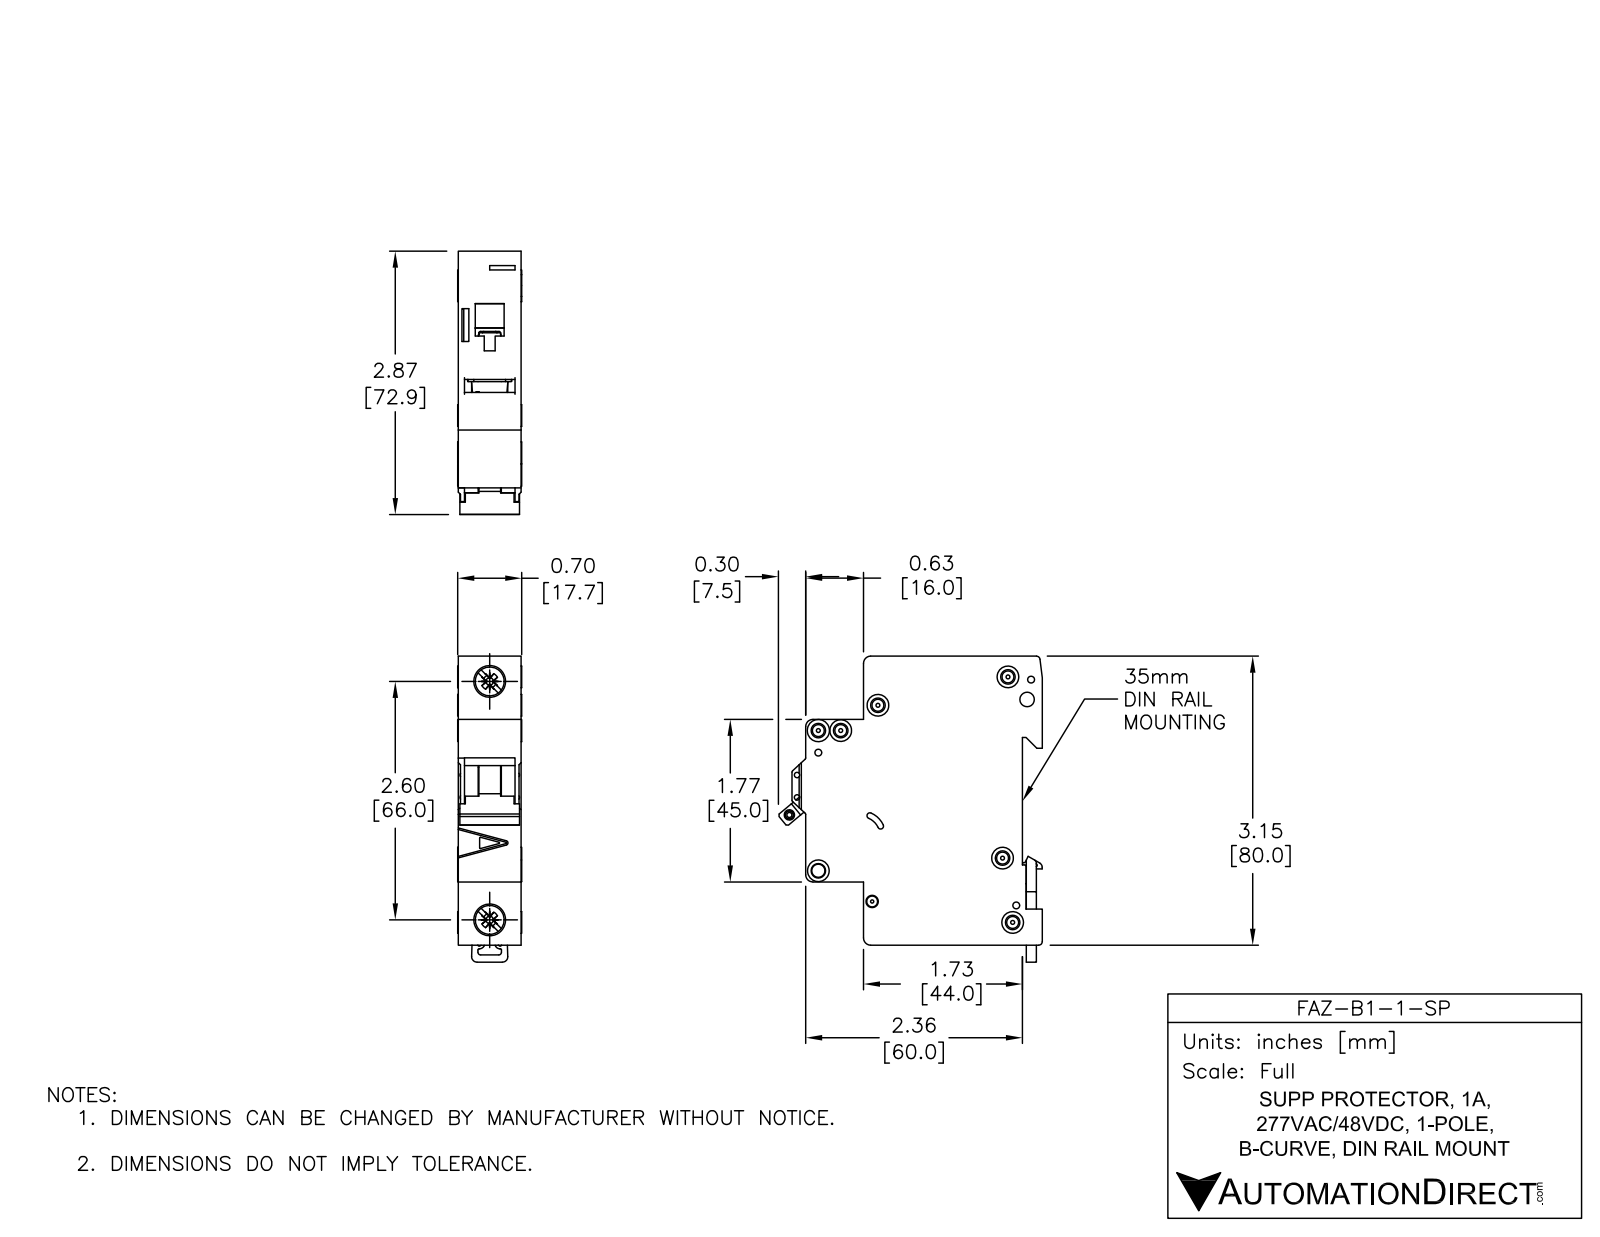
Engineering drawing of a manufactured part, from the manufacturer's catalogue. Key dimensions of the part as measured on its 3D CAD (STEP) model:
Part name (STEP PRODUCT): FAZ-B1-1-SP
STEP written by: SolidWorks 2014 (AUTOMOTIVE_DESIGN)
Units: millimetres
Bodies: 5 solids, 558 faces (235 planar, 202 cylindrical, 121 other)
Overall size (bounding box): 84.78 × 73.04 × 17.7
Volume: 74 935 mm³ · Surface area: 19 545 mm²
Round holes (diameter × count): ⌀3.6 ×6, ⌀1.9 ×3, ⌀1.09 ×2, ⌀1.5 ×2, ⌀4 ×2, ⌀7.15 ×2, ⌀2.15 ×1, ⌀2.2 ×1, ⌀2.55 ×1, ⌀3.3 ×1, ⌀3.4 ×1
Round bosses / shafts (diameter × count): ⌀6 ×4, ⌀8.2 ×2, ⌀2.5 ×1
Partial cylindrical surfaces — rounded edges, fillets, slot ends (radius × count): R0.25 ×30, R0.5 ×13, R2 ×8, R0.2 ×5, R1 ×4, R0.8 ×2, R3 ×2, R1.5 ×1
Main face-to-face distances: 17.5, 79.48, 5.5, 49.5, 44, 65.5, 60, 16, 1.75, 15.75
Hole centre spacings: 6.2, 13.64, 4.81, 5.19, 5.61, 6.1, 6.44, 8.19
